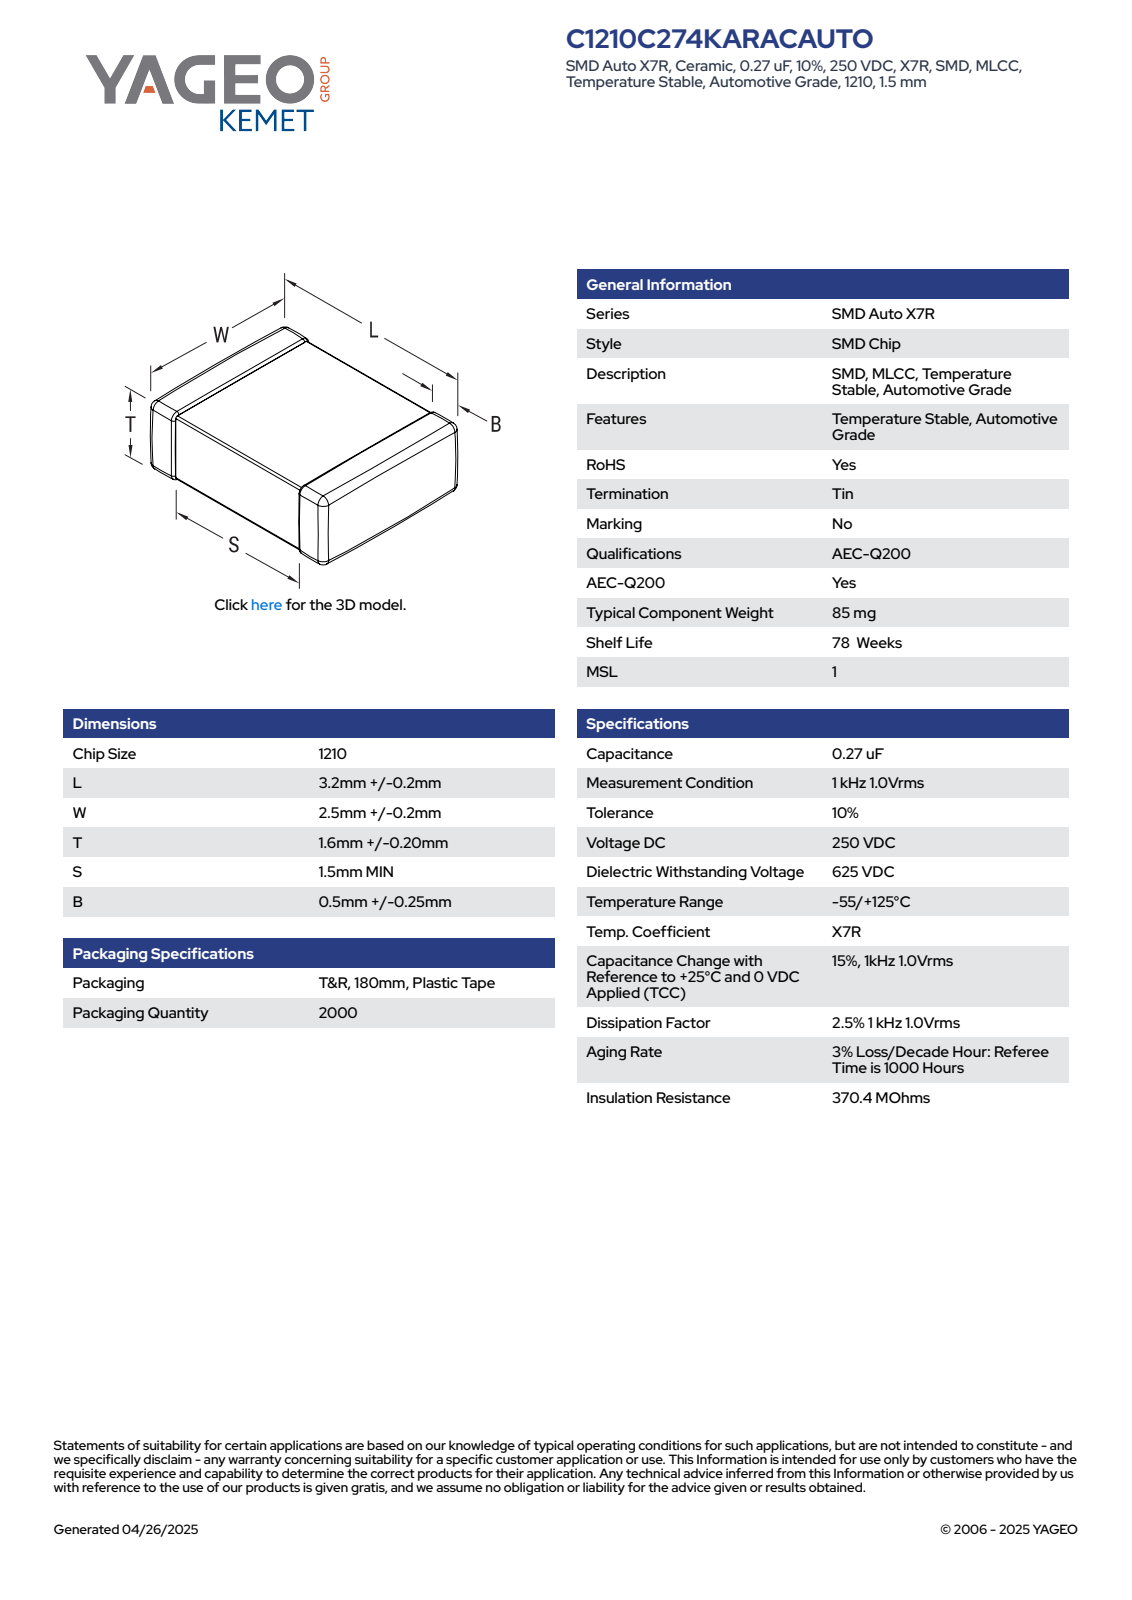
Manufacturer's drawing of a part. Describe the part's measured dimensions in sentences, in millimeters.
The part is named "CCS_CCSTD_1210_L3.4W2.7T1.8B0.5". Its 3-D file was written by "SolidWorks 2021 (AUTOMOTIVE_DESIGN)". It is 4 solids with 125 faces: 71 planar, 38 cylindrical and 16 other. Overall it measures 3.4 by 2.7 by 1.8 millimeters. Its volume is 16 cubic millimeters and its surface area 40 square millimeters. The main face-to-face distances are 1.74, 1.68, 3.4, 2.64, 1.8, 2.58, 2.7, 1.75, 1.69, 0.4.
